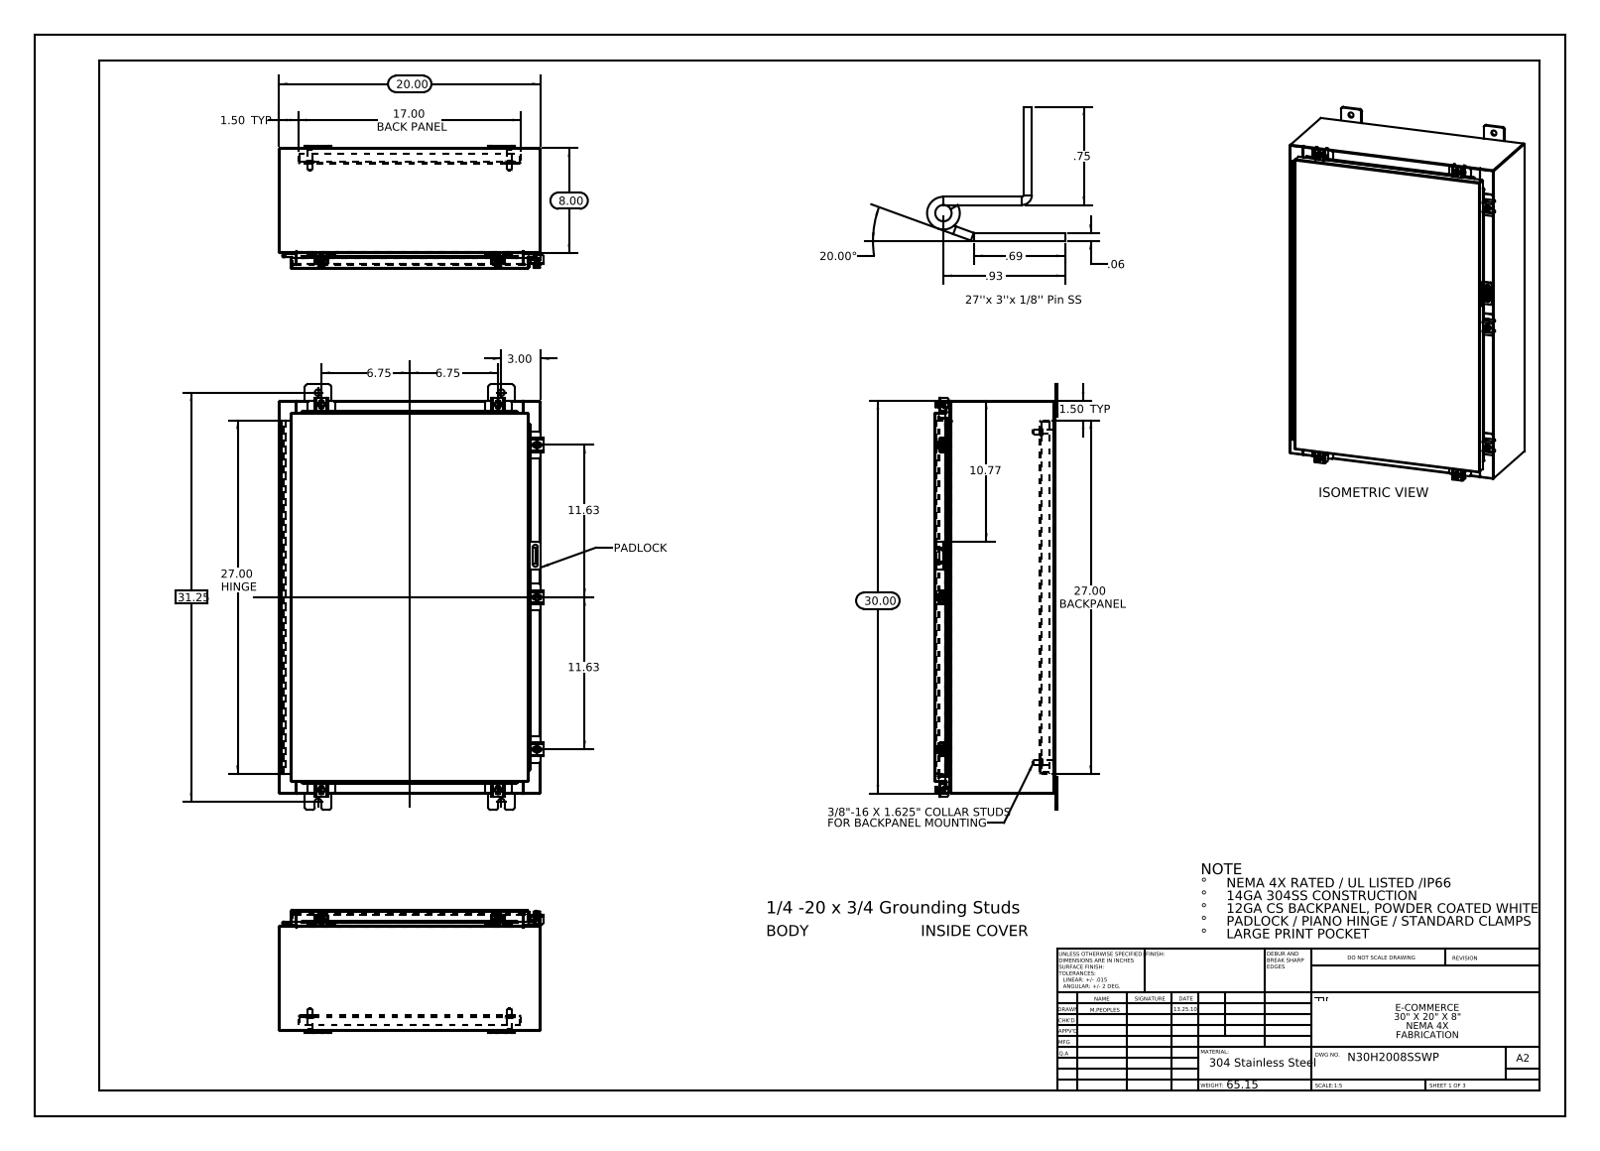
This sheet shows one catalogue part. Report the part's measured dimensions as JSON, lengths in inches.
{"part_name": "N30H2008SSWP 22104005_DEFAULT; N30H2008SSWP Hinge Cover Side; N30H2008SSWP Clamp Bracket; N30H2008SSWP Padlock Hasp (+8 more)", "step_written_by": "SolidWorks 2013 (CONFIG_CONTROL_DESIGN)", "units": "inches", "bodies": {"solids": 52, "faces": 1990, "planar": 1056, "cylindrical": 830, "other": 104}, "overall_size": [32.5, 20.211, 9.389], "volume_in3": 229, "surface_area_in2": 5746, "round_holes": [[0.5, 8], [0.213, 7], [0.26, 7], [0.125, 2], [0.125, 1]], "round_bosses_or_shafts": [[0.25, 8], [0.5, 7], [0.399, 7], [0.625, 4], [0.375, 4], [0.33, 4]], "partial_cylinders_radius": [[0.06, 34], [0.013, 27], [0.19, 24], [0.088, 21], [0.12, 14], [0.141, 14], [0.05, 11], [0.08, 10]], "face_to_face_distances": [0.075, 9.126, 9.201, 9.051, 0.104, 19.925, 1, 1.075, 8.051, 8.126], "hole_center_spacings": [27.365, 30.898, 0.431, 0.934, 1.858, 2.275, 2.276, 2.327]}
